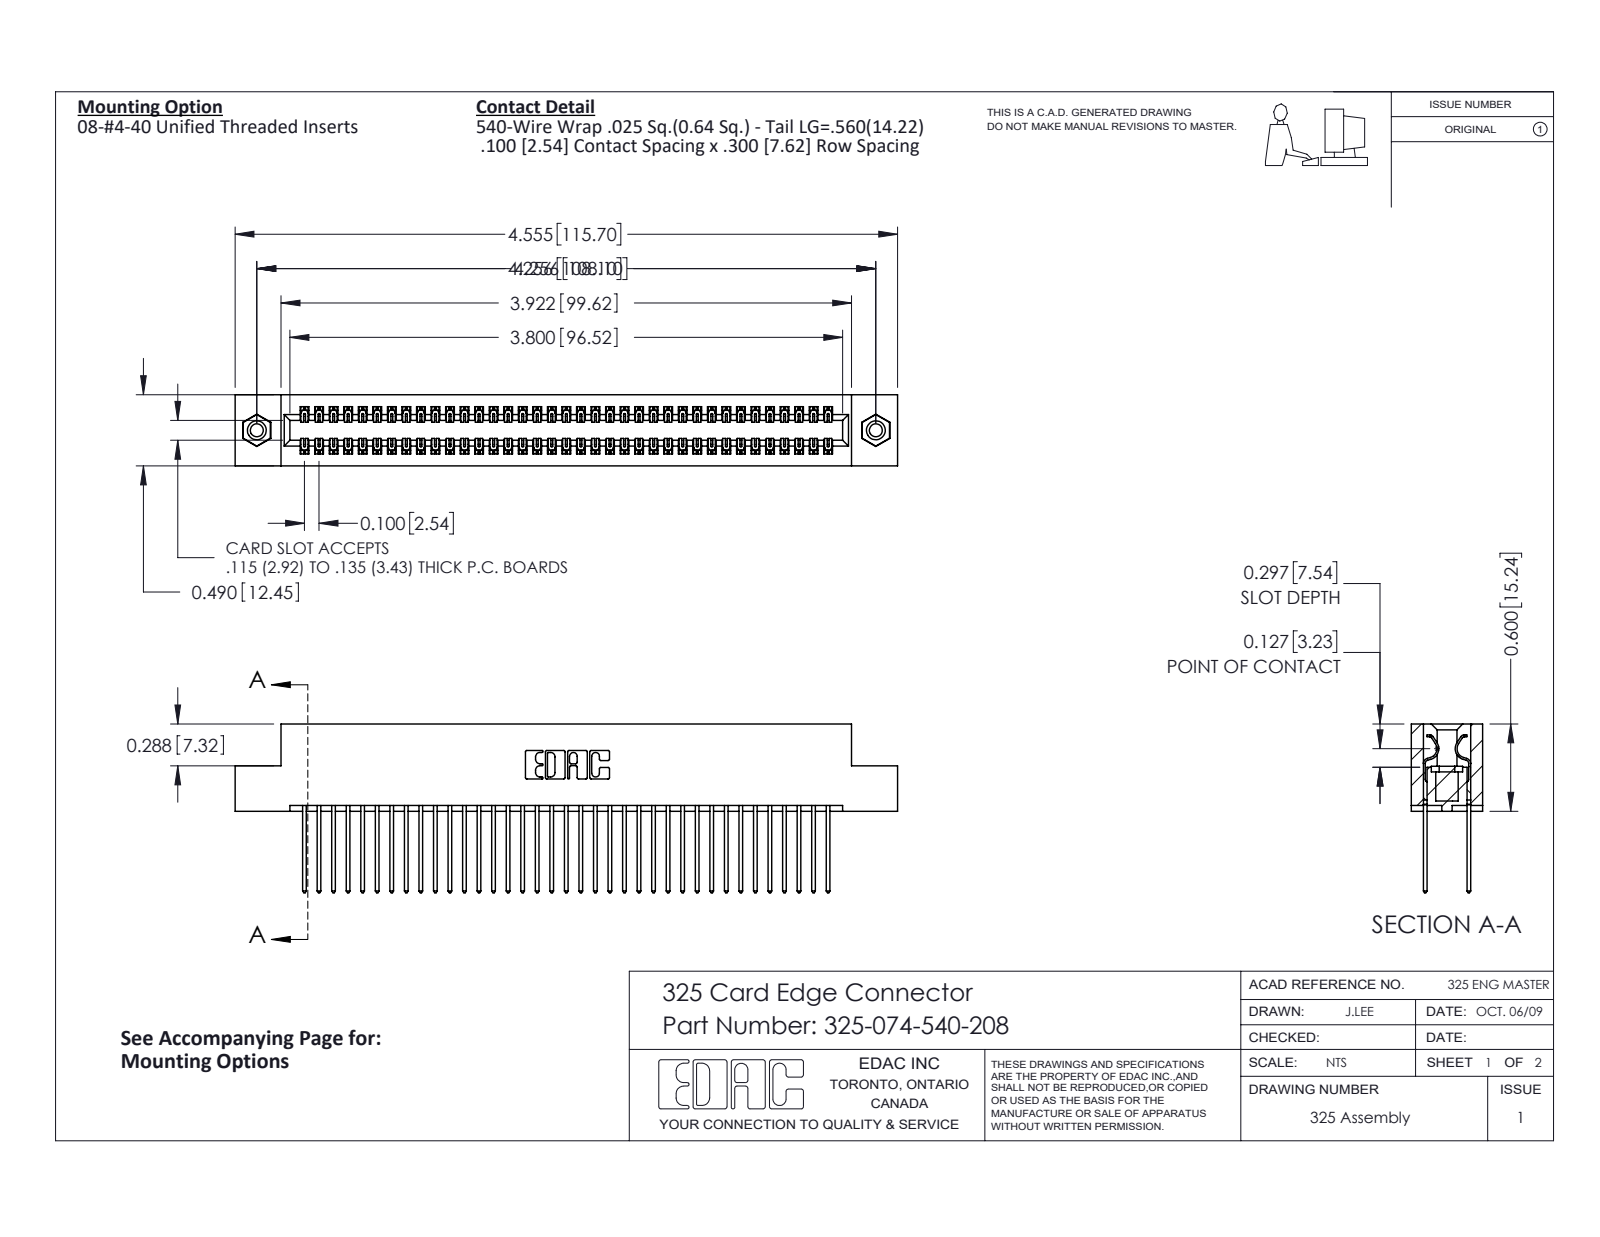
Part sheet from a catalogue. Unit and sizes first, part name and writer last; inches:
Units: inches
Overall size (bounding box): 4.555 × 1.16 × 0.49
Round holes (diameter × count): ⌀0.089 ×2, ⌀0.125 ×2, ⌀0.16 ×2
Round bosses / shafts (diameter × count): ⌀0.155 ×2
Partial cylindrical surfaces — rounded edges, fillets, slot ends (radius × count): R0.006 ×111, R0.01 ×74, R0.01 ×22, R0.007 ×6, R0.031 ×6, R0.026 ×3, R0.014 ×2, R0.022 ×2
Main face-to-face distances: 0.083, 0.407, 0.3, 0.107, 0.383, 0.025, 0.49, 0.325, 0.275, 0.56
Hole centre spacings: 4.256
Volume: 0.925 in³ · Surface area: 30.36 in²
Bodies: 77 solids, 4022 faces (2766 planar, 1240 cylindrical, 16 other)
Part name (STEP PRODUCT): 345-250-001_345-250-003-102; 325-074-540-208; 325 Part_TI; 325-292-001_325-293-140
STEP written by: SolidWorks 2016 (CONFIG_CONTROL_DESIGN)
